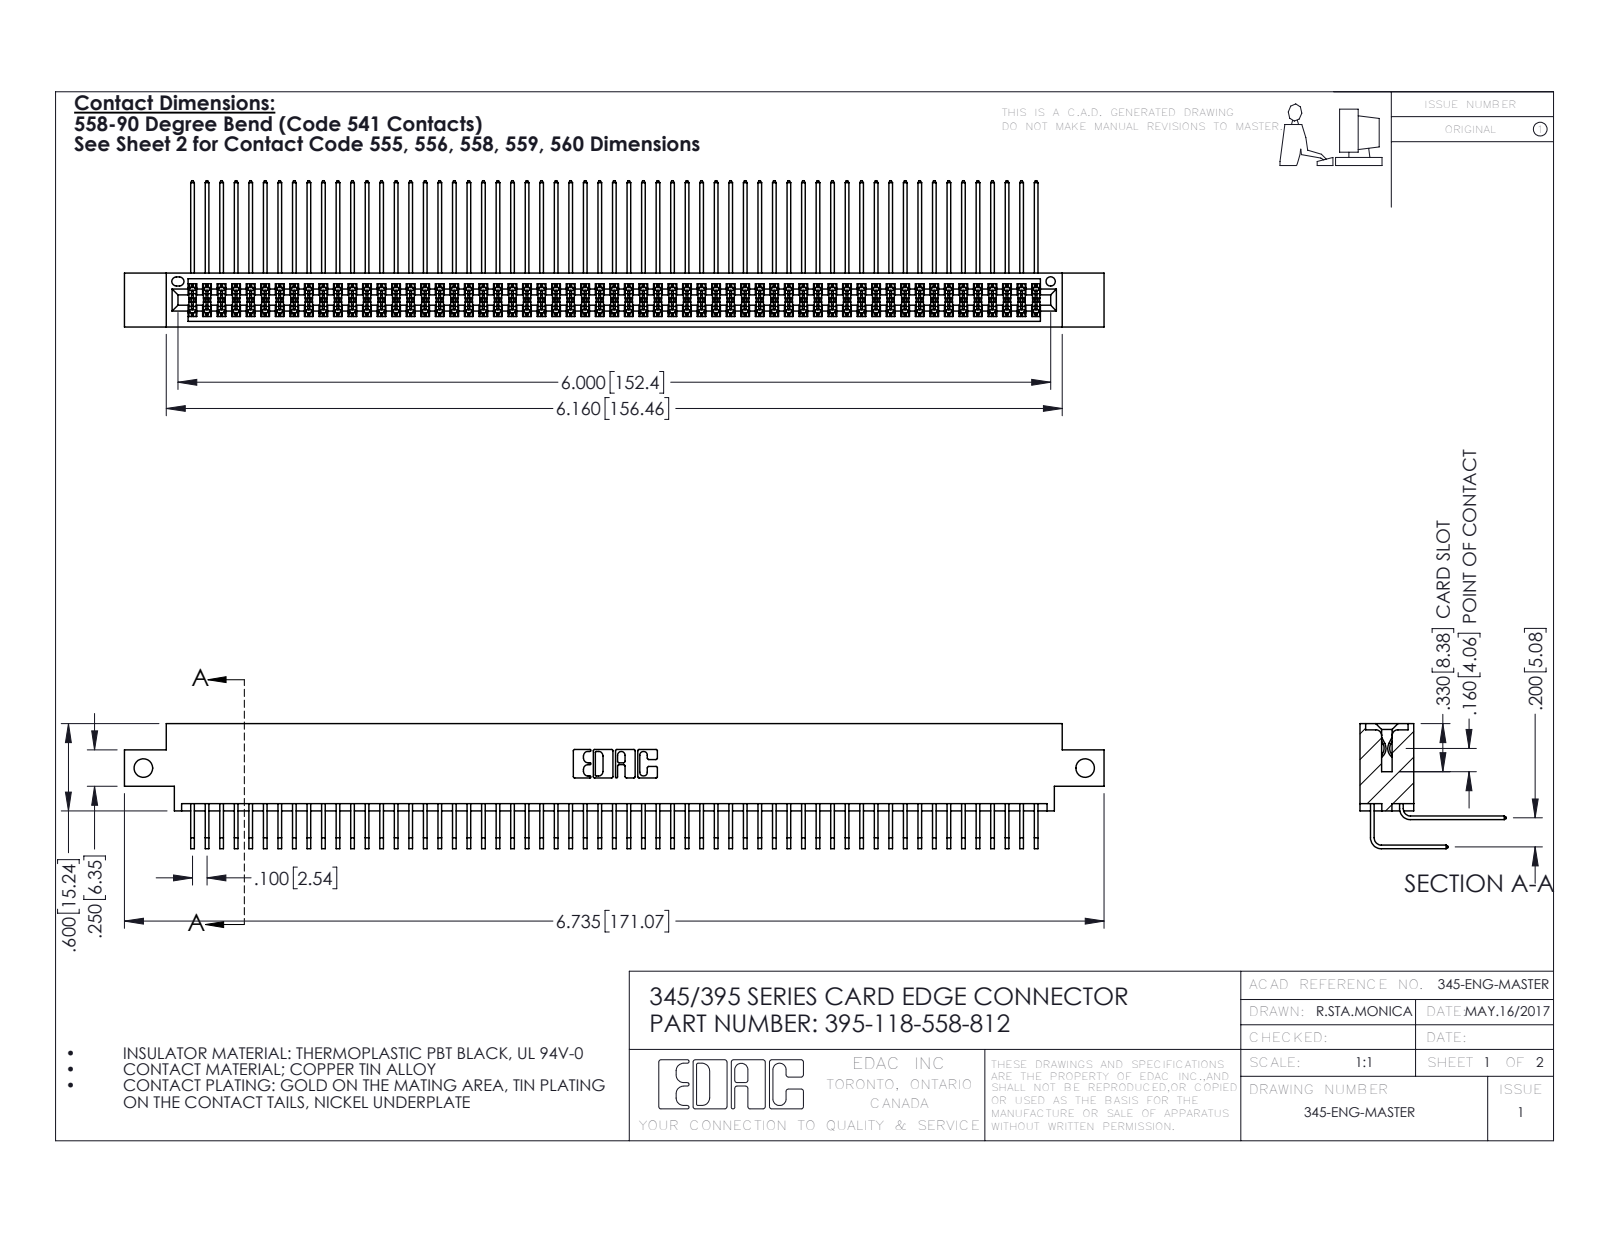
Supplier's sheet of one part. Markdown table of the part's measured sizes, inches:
| quantity | value |
| --- | --- |
| part name | 395-118-558-812; 345-292-001_558 Tail - 2; 345 Part_0.170 Offset - Side Mount; 345-292-001_558 559 Tail - 1 |
| STEP written by | SolidWorks 2016 (CONFIG_CONTROL_DESIGN) |
| units | inches |
| bodies | 119 solids, 6266 faces (4214 planar, 2052 cylindrical, 0 other) |
| overall size | 6.735 × 1.005 × 0.859 |
| volume | 1.053 in³ |
| surface area | 45.02 in² |
| round holes (diameter × count) | 0.128 × 2, 0.064 × 1 |
| partial cylindrical surfaces (radius × count) | 0.006 × 178, 0.01 × 22, 0.007 × 6, 0.031 × 6, 0.026 × 3, 0.014 × 2, 0.019 × 2, 0.022 × 2 |
| main face-to-face distances | 0.072, 0.298, 0.2, 0.37, 0.098, 0.272, 0.025, 0.225, 0.175, 0.025 |
| hole center spacings | 6.475 |
